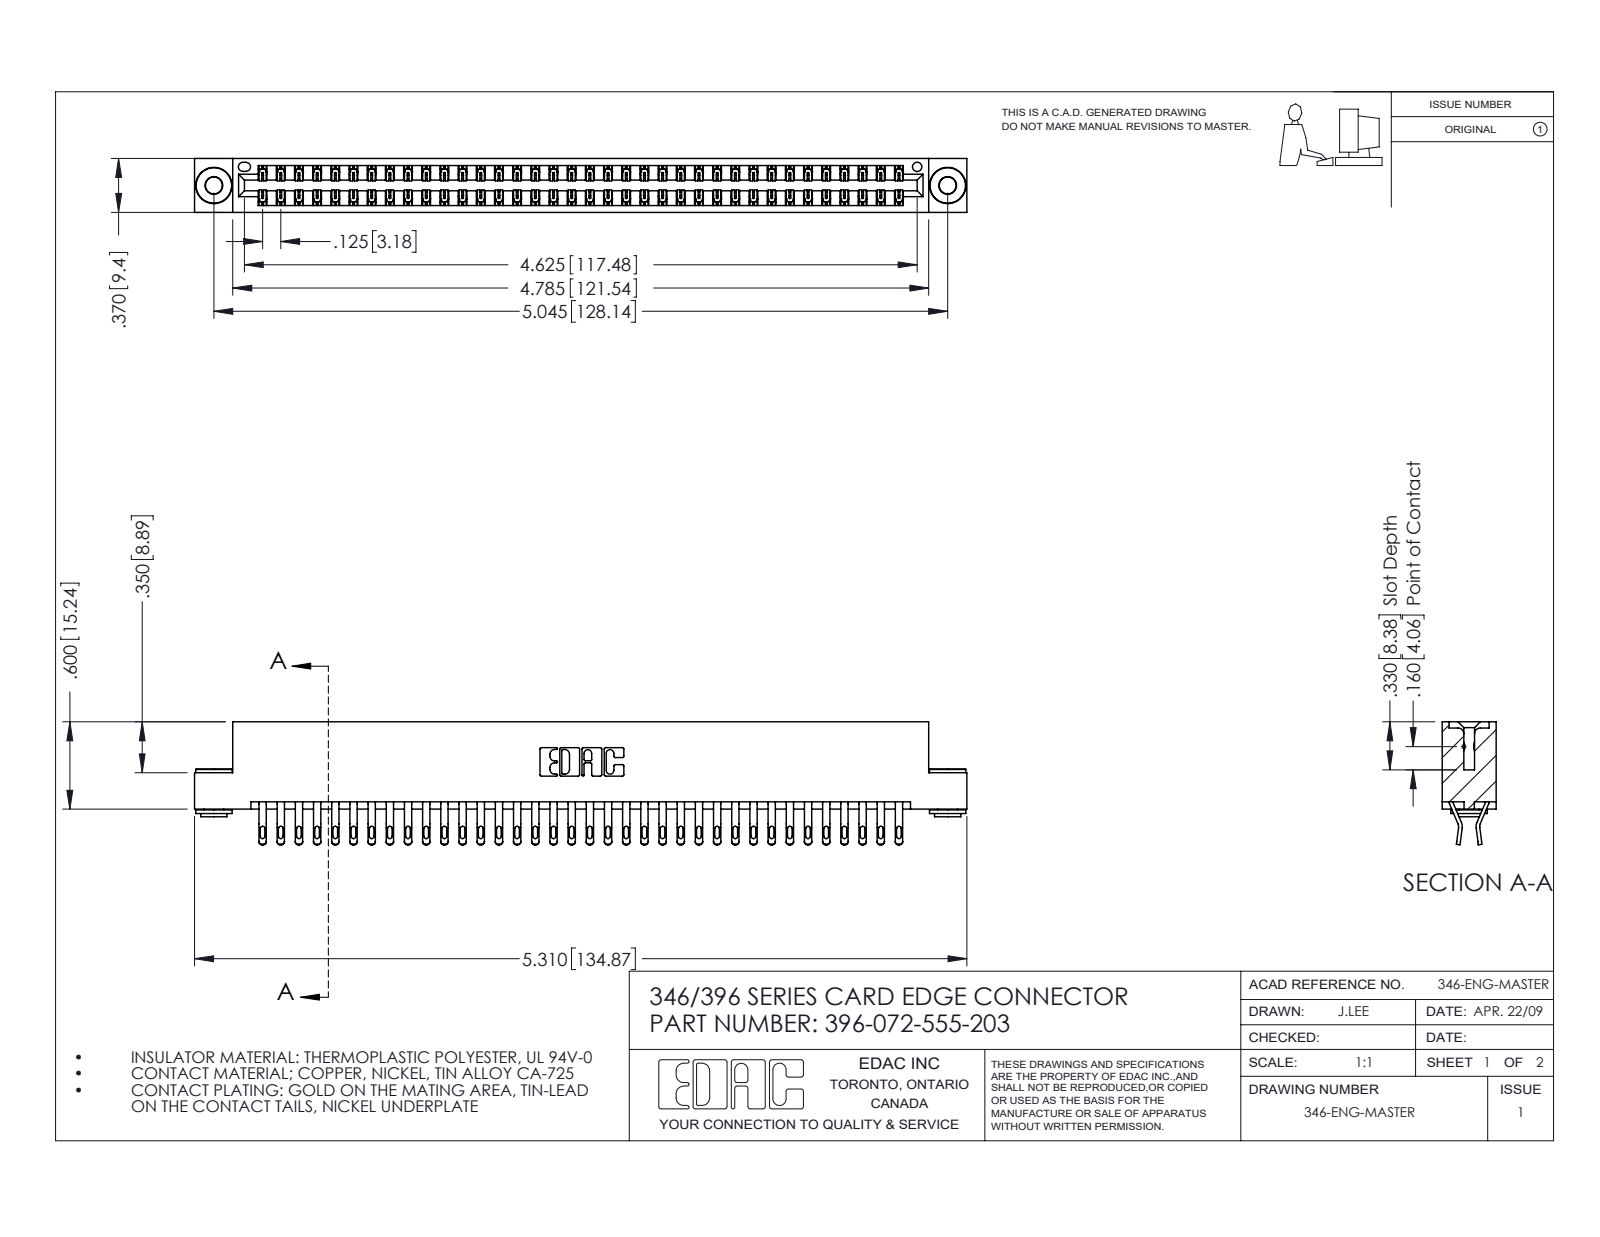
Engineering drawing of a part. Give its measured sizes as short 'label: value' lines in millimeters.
name: 396-072-555-203; 345-250-002_345-250-002-102; 346 Part_Flush Mounting Lugs - 0.156 Dia-TH; 345-292-001_555 Tail
written by: SolidWorks 2016 (CONFIG_CONTROL_DESIGN)
unit: mm
bodies: 75 solids, 4336 faces (2462 planar, 1866 cylindrical, 8 other)
size: 134.9 × 21.5 × 9.4
volume: 13 300 mm³; area: 19 190 mm²
holes: 2× ⌀2.9, 2× ⌀4, 1× ⌀1.6
bosses: 2× ⌀6.4, 2× ⌀4.6, 2× ⌀3.5
rounds: 144× R0.4, 144× R0.5, 108× R0.2, 22× R0.3, 6× R0.2, 6× R0.8, 3× R0.7, 2× R0.3
face distances: 1.2, 8.2, 9.4, 6.4, 0.6, 1.8, 7.6, 7, 3.8, 5.6
hole spacings: 6.2, 122.8, 128.1
